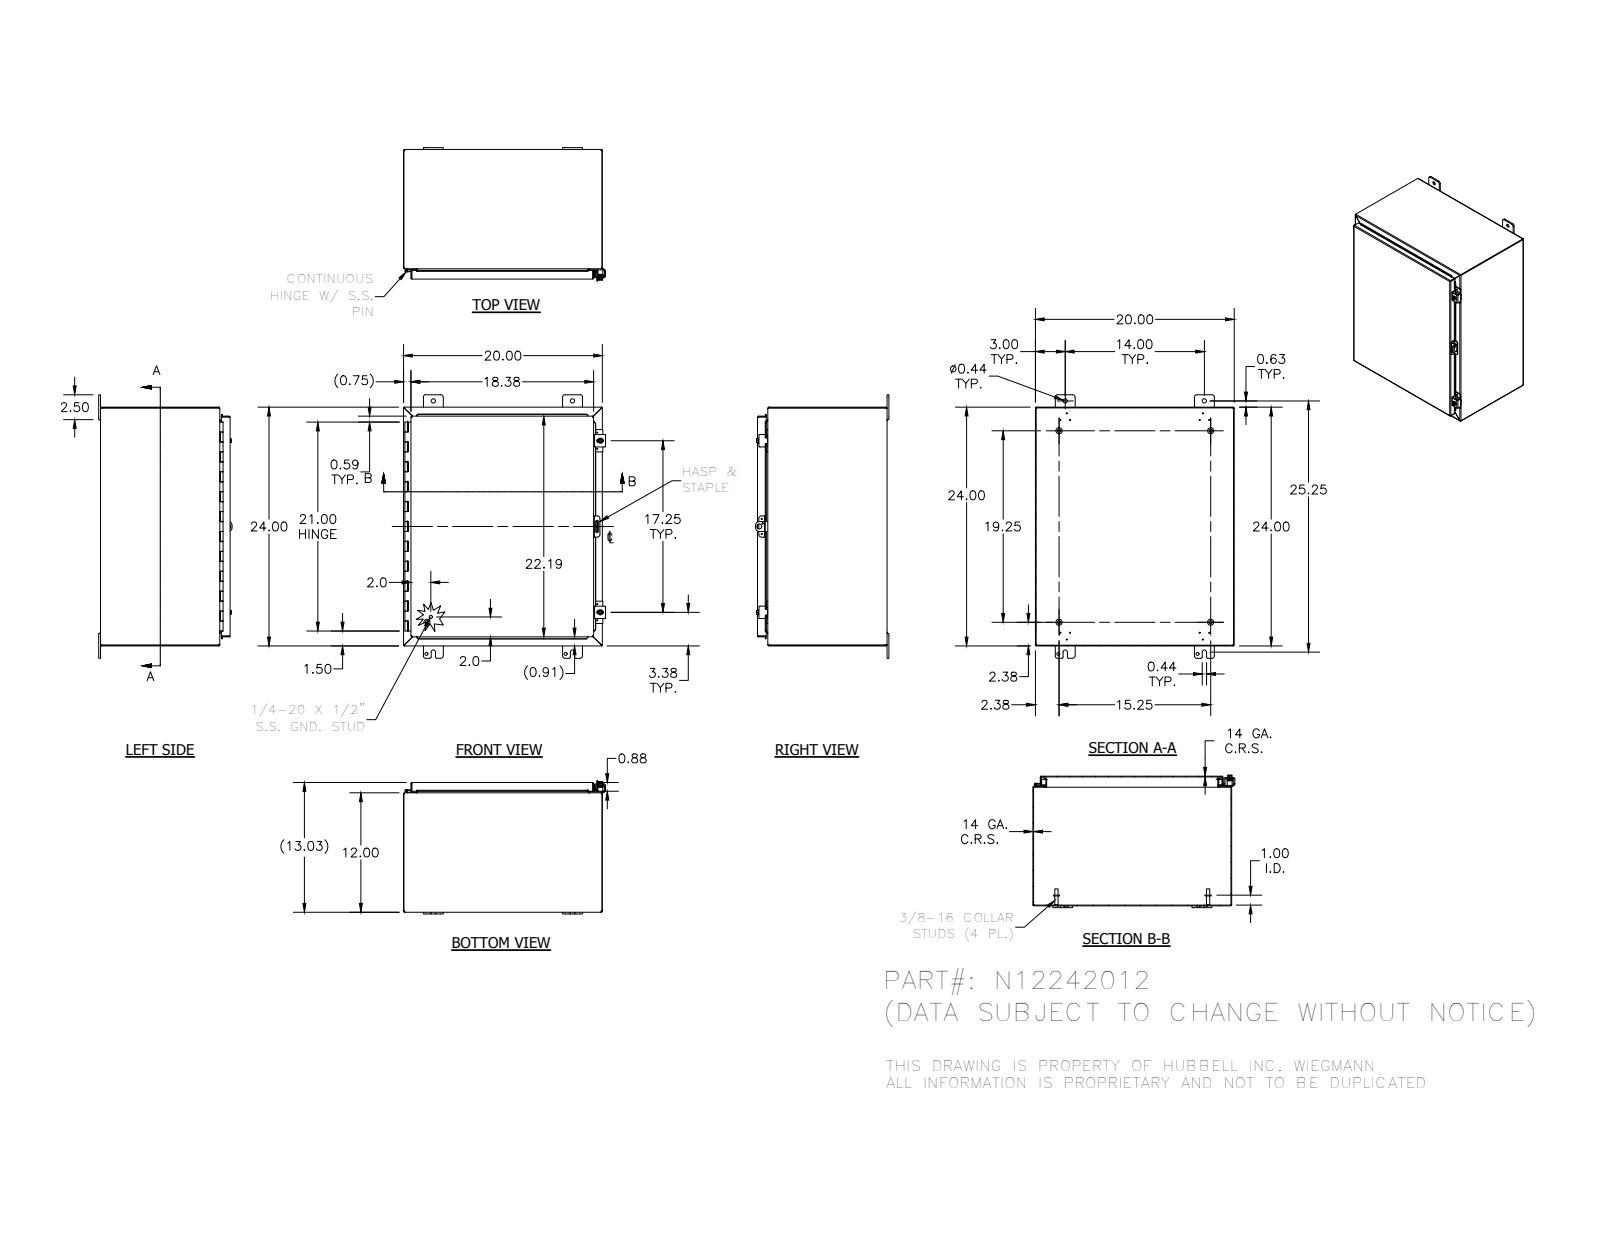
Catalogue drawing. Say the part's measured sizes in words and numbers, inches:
The part is named "N12242012; 34840; 38420; N12242012BKP (+8 more)". Its 3-D file was written by "Autodesk Inventor 2012 (AUTOMOTIVE_DESIGN)". It is 27 solids with 982 faces: 533 planar, 332 cylindrical and 117 other. Overall it measures 26.5 by 20.311 by 13.41 inches. Its volume is 178.2 cubic inches and its surface area 4 677 square inches. Round holes: 12 of diameter 0.12, 7 of diameter 0.11, 4 of diameter 0.313, 4 of diameter 0.438, 2 of diameter 0.211, 2 of diameter 0.281, 2 of diameter 0.3, 1 of diameter 0.125, 1 of diameter 0.156, 1 of diameter 0.5. Round bosses or shafts: 4 of diameter 0.625, 4 of diameter 0.33, 4 of diameter 0.25, 2 of diameter 0.52, 2 of diameter 0.5, 2 of diameter 0.35, 2 of diameter 0.115, 1 of diameter 0.337. Partial cylindrical surfaces (rounded edges, fillets, slot ends): 27 of radius 0.03, 25 of radius 0.063, 25 of radius 0.125, 25 of radius 0.25, 23 of radius 0.031, 23 of radius 0.105, 8 of radius 0.07, 4 of radius 0.1. The main face-to-face distances are 0.074, 12.959, 19.926, 23.926, 12.885, 13.033, 20, 19.852, 24, 23.852. The hole center spacings are 14, 0.759, 0.839, 0.94, 0.969, 13.375, 14.342, 21.38.
